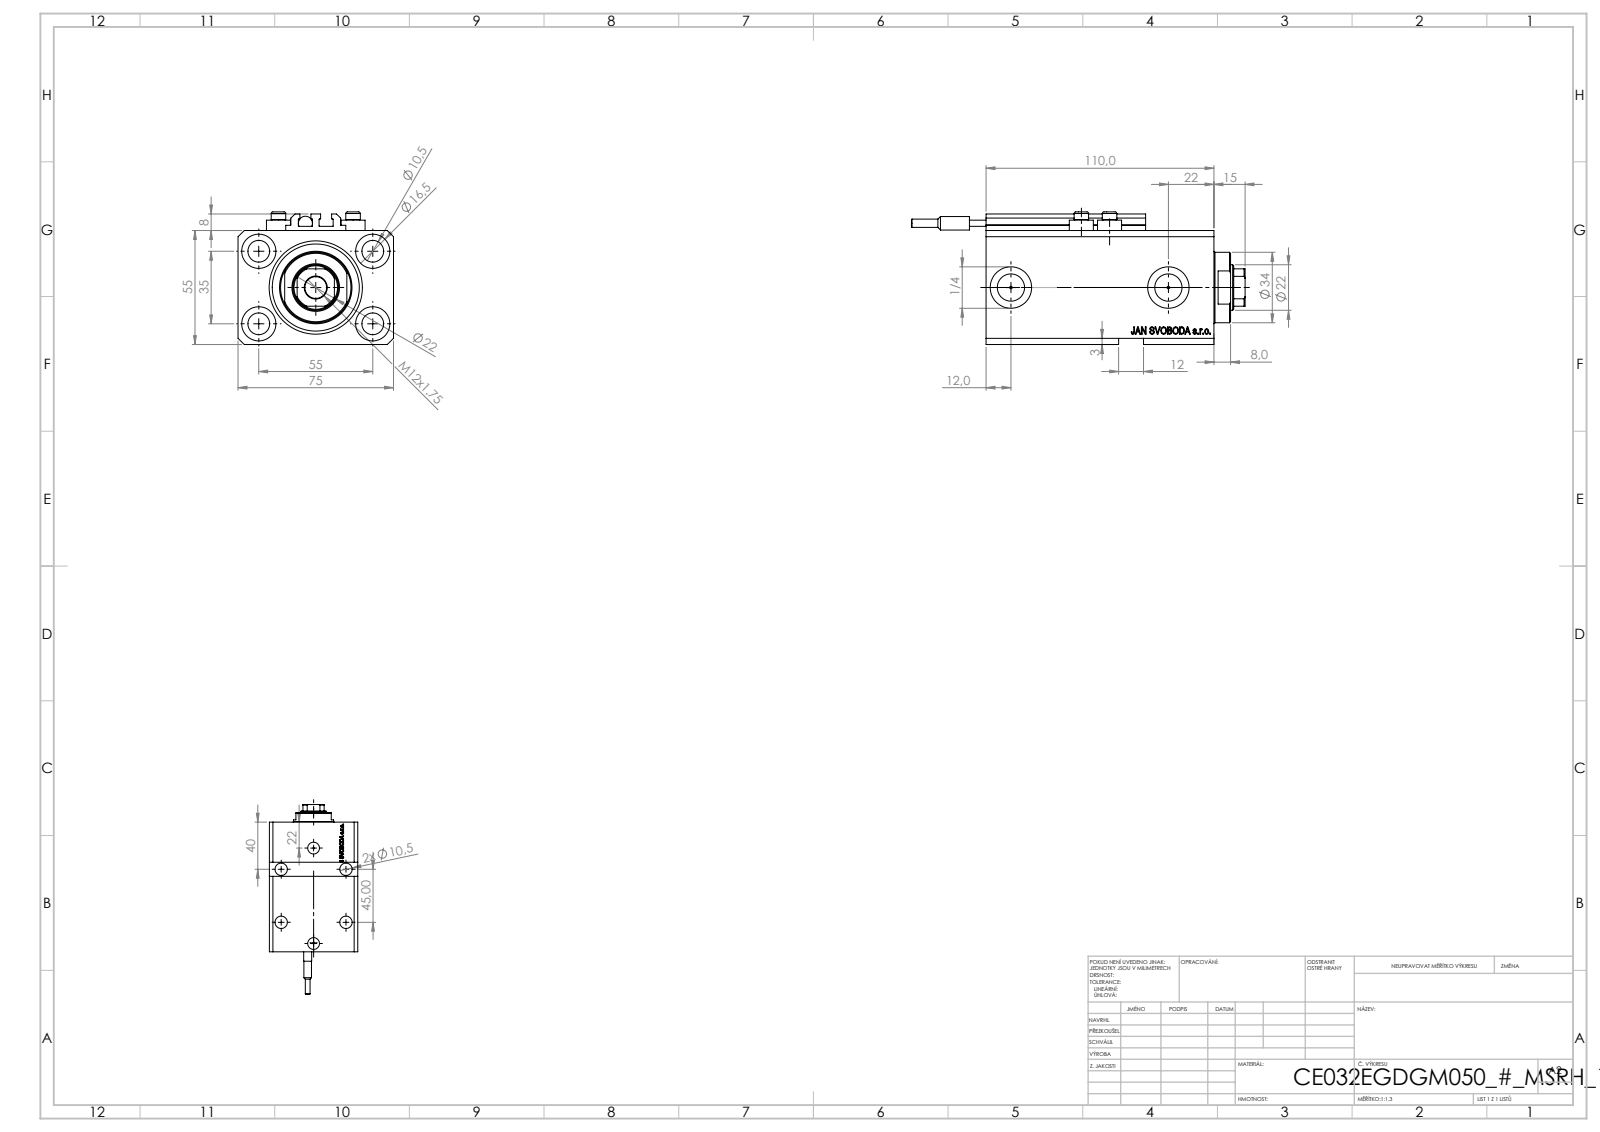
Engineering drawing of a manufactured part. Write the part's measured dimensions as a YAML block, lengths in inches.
part_name: "V250CE_VC_E; V250CE_E_Body; SWITCH_V250CE; ALLEN BOLT V250CE (+1 more)"
step_written_by: "SolidWorks 2019 (CONFIG_CONTROL_DESIGN)"
units: inches
bodies: {solids: 9, faces: 1126, planar: 534, cylindrical: 164, other: 428}
overall_size: [6.339, 2.953, 2.52]
volume: 23.16
surface_area: 152.2
round_holes:
  - {diameter: 0.413, count: 9}
  - {diameter: 0.049, count: 4}
  - {diameter: 0.157, count: 4}
  - {diameter: 0.65, count: 4}
  - {diameter: 0.394, count: 2}
  - {diameter: 0.518, count: 2}
  - {diameter: 0.787, count: 2}
  - {diameter: 0.866, count: 1}
  - {diameter: 1.26, count: 1}
  - {diameter: 1.772, count: 1}
round_bosses_or_shafts:
  - {diameter: 0.457, count: 4}
  - {diameter: 0.276, count: 4}
  - {diameter: 1.339, count: 1}
  - {diameter: 0.268, count: 1}
  - {diameter: 0.256, count: 1}
  - {diameter: 0.157, count: 1}
partial_cylinders:
  - {radius: 0.008, count: 10}
  - {radius: 0.413, count: 1}
face_to_face_distances: [2.165, 2.953, 0.591, 0.118, 4.331, 3.74, 0.39, 2.244, 3.35, 3.941]
hole_center_spacings: [1.283, 1.294, 2.165, 2.706, 0.535, 0.555, 0.907, 1.016]
